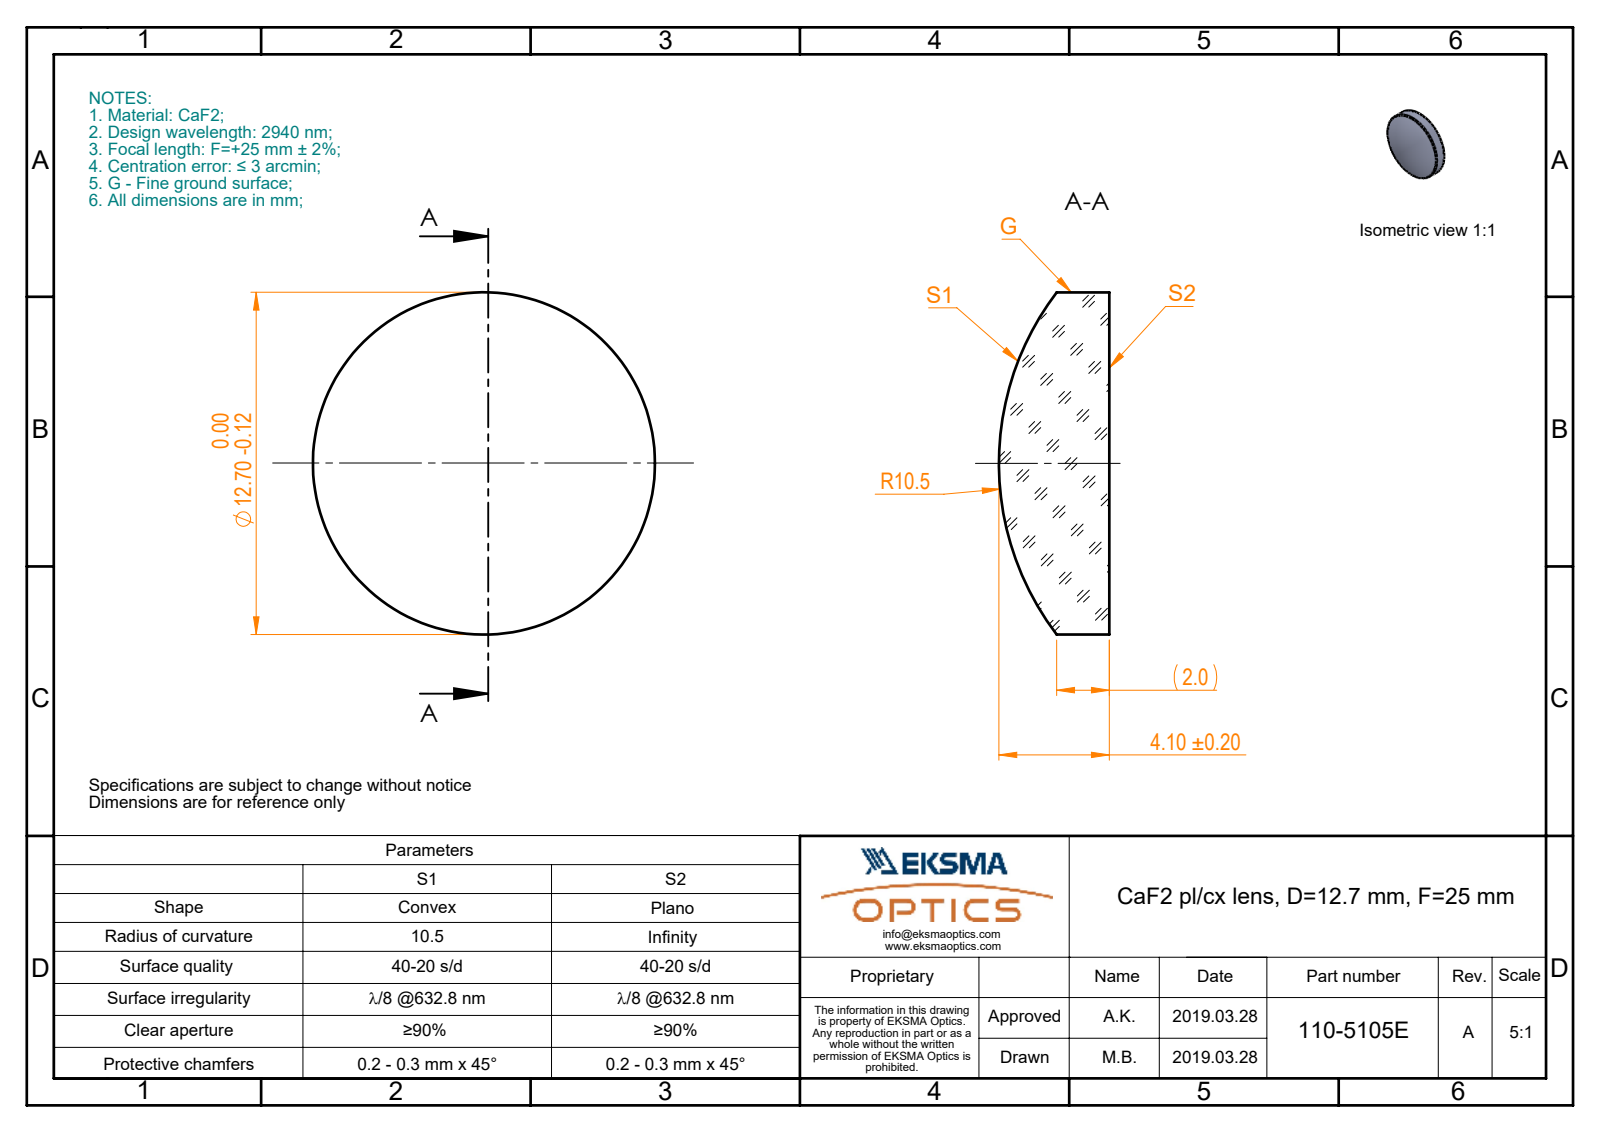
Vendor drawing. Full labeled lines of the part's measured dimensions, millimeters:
Part name (STEP PRODUCT): 110-5105E CaF2 pl-cx 12.7 F25
STEP written by: SolidWorks 2017 (CONFIG_CONTROL_DESIGN)
Units: millimetres
Bodies: 1 solid, 5 faces (1 planar, 2 cylindrical, 2 other)
Overall size (bounding box): 12.7 × 12.7 × 4.1
Volume: 389 mm³ · Surface area: 346 mm²
Round bosses / shafts (diameter × count): ⌀12.7 ×1
